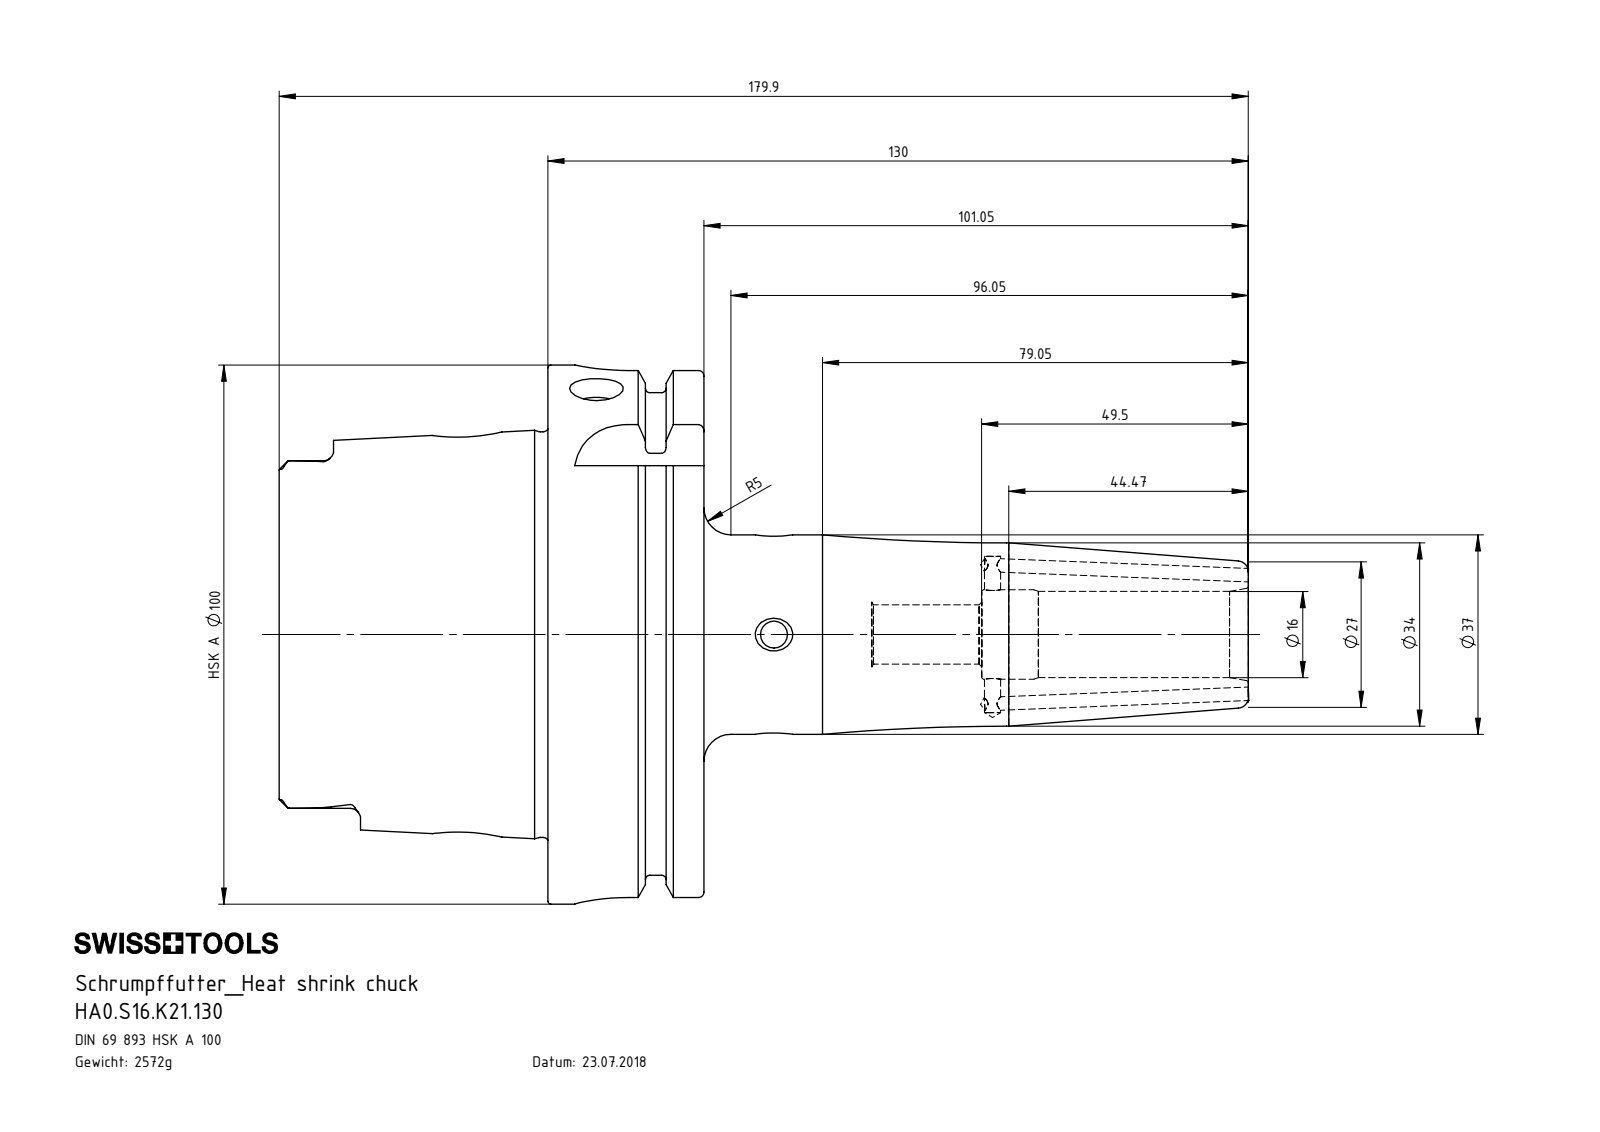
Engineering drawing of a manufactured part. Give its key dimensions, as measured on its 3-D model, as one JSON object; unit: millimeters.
{"part_name": "HA0-S16.K21.130_C_Fertigbearbeitung; ERU-AN5.K01.020_A; ERU-CJ2.001.006; HA0.S16.K21.130", "step_written_by": "SolidWorks 2017 (CONFIG_CONTROL_DESIGN)", "units": "millimeters", "bodies": {"solids": 4, "faces": 303, "planar": 95, "cylindrical": 88, "other": 120}, "overall_size": [179.98, 100, 100], "volume_mm3": 327633, "surface_area_mm2": 66703, "round_holes": [[10, 3], [2.5, 2], [5, 2], [12, 2], [3, 1], [6, 1], [11, 1], [16, 1], [16.6, 1], [22.5, 1], [26, 1], [53, 1]], "round_bosses_or_shafts": [[3, 2], [100, 1], [91.95, 1], [75.26, 1], [37, 1], [34, 1]], "partial_cylinders_radius": [[1.9, 6], [4.88, 4], [10, 4]], "face_to_face_distances": [28.95, 12.45, 16.5, 49.9, 62.35, 78.85, 87.8, 78.2, 28.3, 15.85], "hole_center_spacings": [34.95, 40.55, 56.95, 97.5]}
